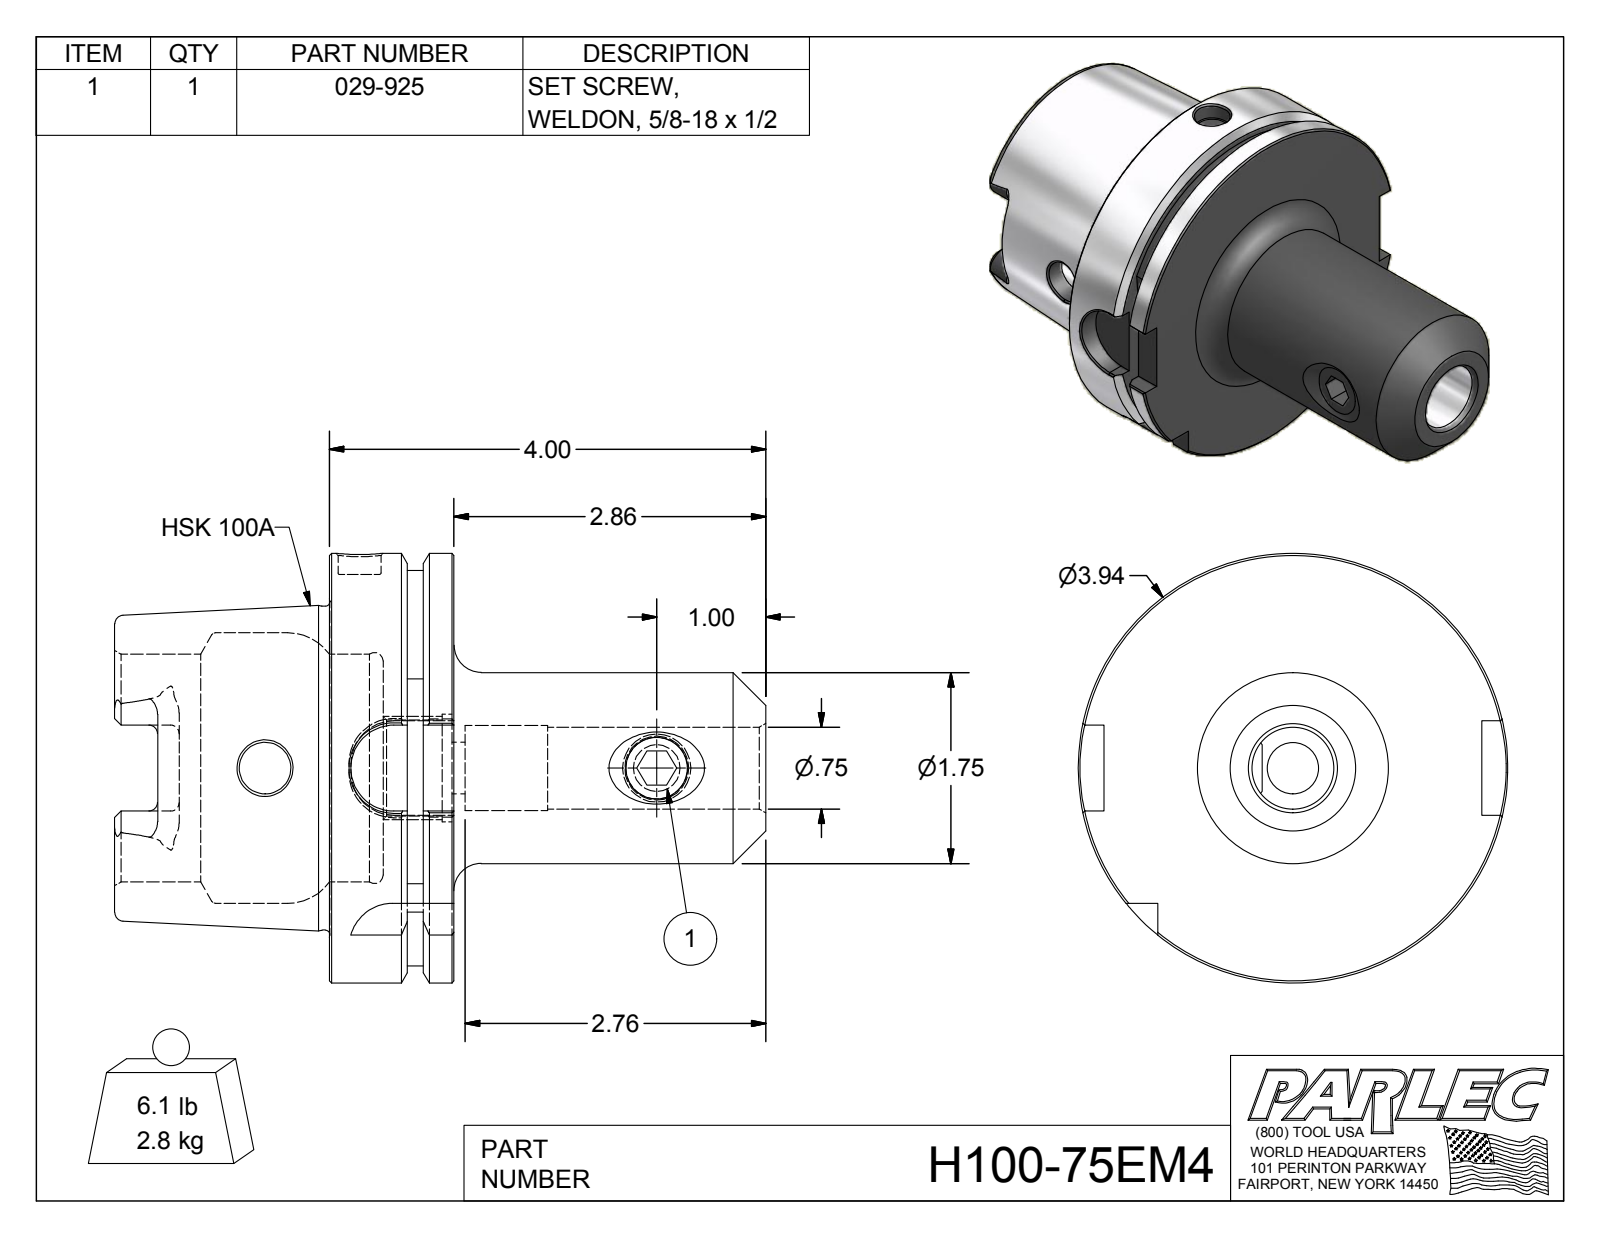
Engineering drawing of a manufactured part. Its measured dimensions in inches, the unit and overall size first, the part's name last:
Units: inches
Overall size (bounding box): 5.969 × 3.937 × 3.937
Round holes (diameter × count): ⌀0.472 ×2, ⌀0.394 ×1, ⌀0.565 ×1, ⌀0.75 ×1, ⌀0.78 ×1, ⌀0.881 ×1, ⌀0.985 ×1, ⌀2.087 ×1, ⌀2.48 ×1
Round bosses / shafts (diameter × count): ⌀3.937 ×1, ⌀2.967 ×1, ⌀1.75 ×1, ⌀0.625 ×1
Partial cylindrical surfaces — rounded edges, fillets, slot ends (radius × count): R0.079 ×6, R0.192 ×4, R0.394 ×4, R1.811 ×1
Main face-to-face distances: 1.142, 0.492, 0.65, 1.969, 2.461, 3.11, 2.83, 0.861, 0.369, 0.28
Hole centre spacings: 3.591
Volume: 20.93 in³ · Surface area: 100.3 in²
Bodies: 2 solids, 139 faces (53 planar, 36 cylindrical, 50 other)
Part name (STEP PRODUCT): H100-75EM4-1; 029-925
STEP written by: Autodesk Inventor 2012 (AUTOMOTIVE_DESIGN)
